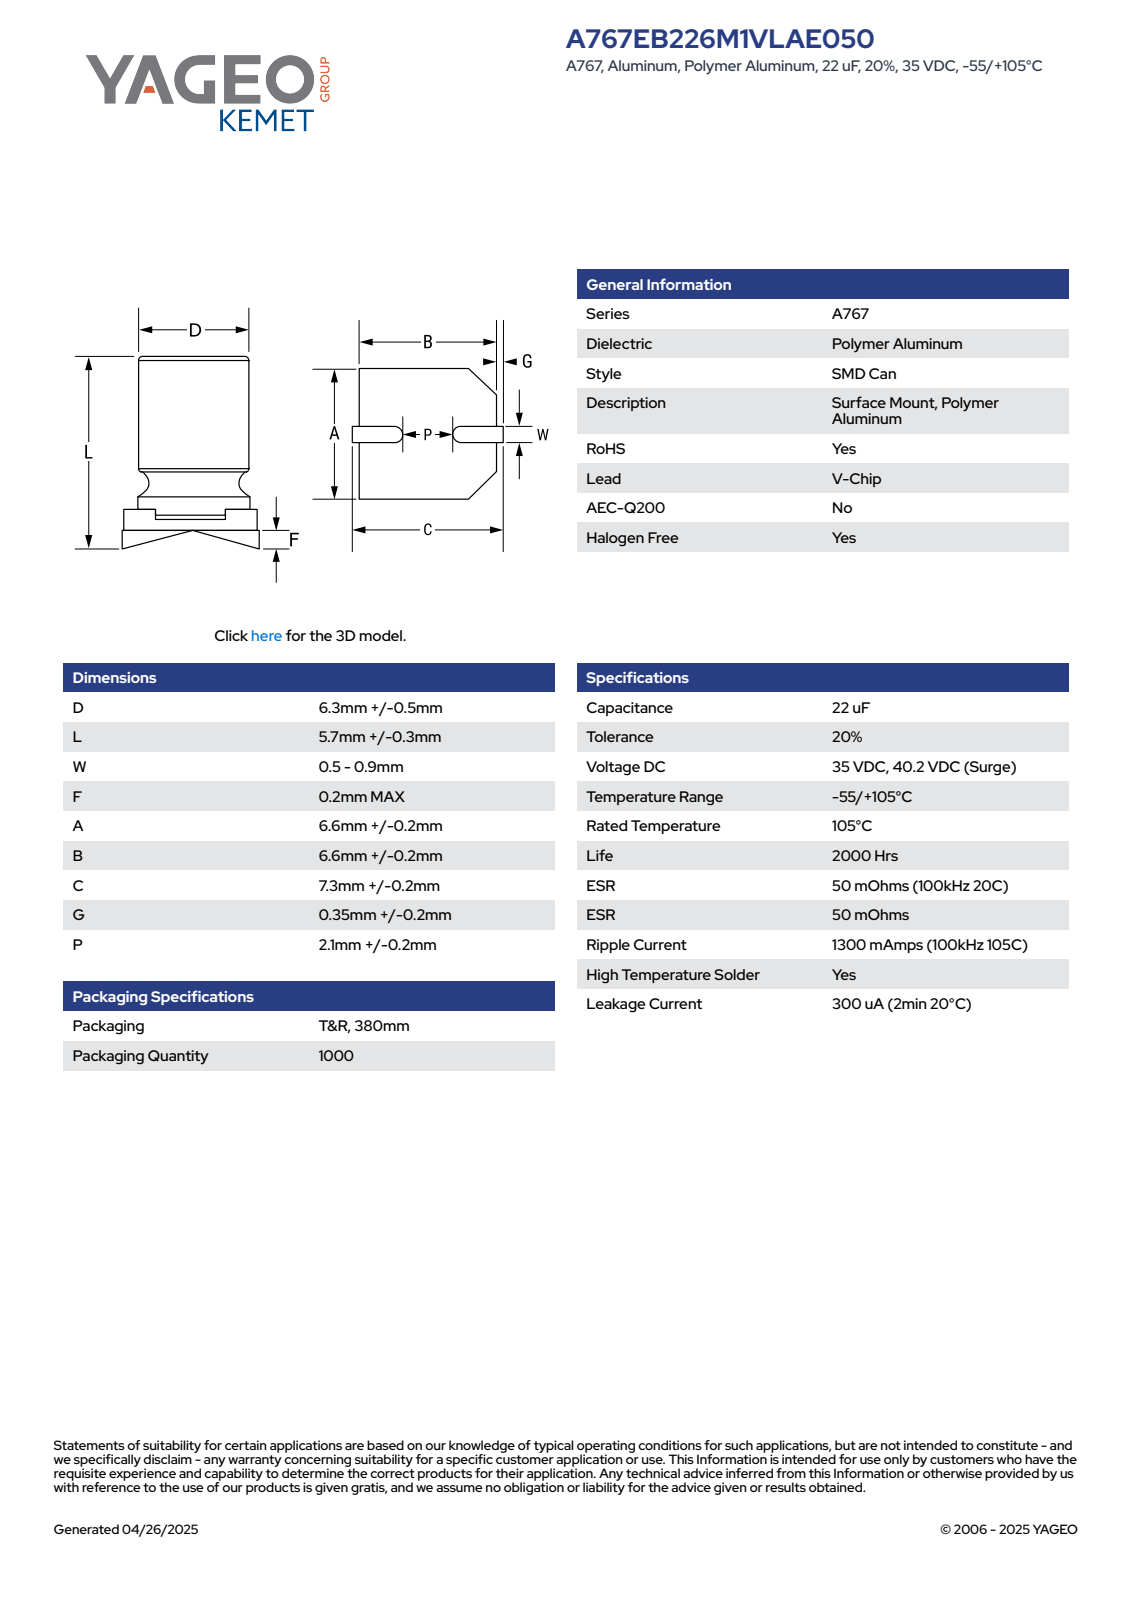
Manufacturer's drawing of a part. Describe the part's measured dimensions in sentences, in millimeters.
The part is named "CAC_KS_6.3X5.7_D6.8L6W0.9F0.2A6.8B6.8C7.5P2.3". Its 3-D file was written by "SolidWorks 2014 (AUTOMOTIVE_DESIGN)". It is 5 solids with 76 faces: 59 planar, 11 cylindrical and 6 other. Overall it measures 7.5 by 6.8 by 6 millimeters. Its volume is 201 cubic millimeters and its surface area 309 square millimeters. Round bosses or shafts: 1 of diameter 6.5. Partial cylindrical surfaces (rounded edges, fillets, slot ends): 2 of radius 0.2, 1 of radius 2.7, 1 of radius 3.4. The main face-to-face distances are 5.8, 5.5, 1.2, 0.5, 6.8, 4.8, 4.3, 1.5, 1.7, 6.
